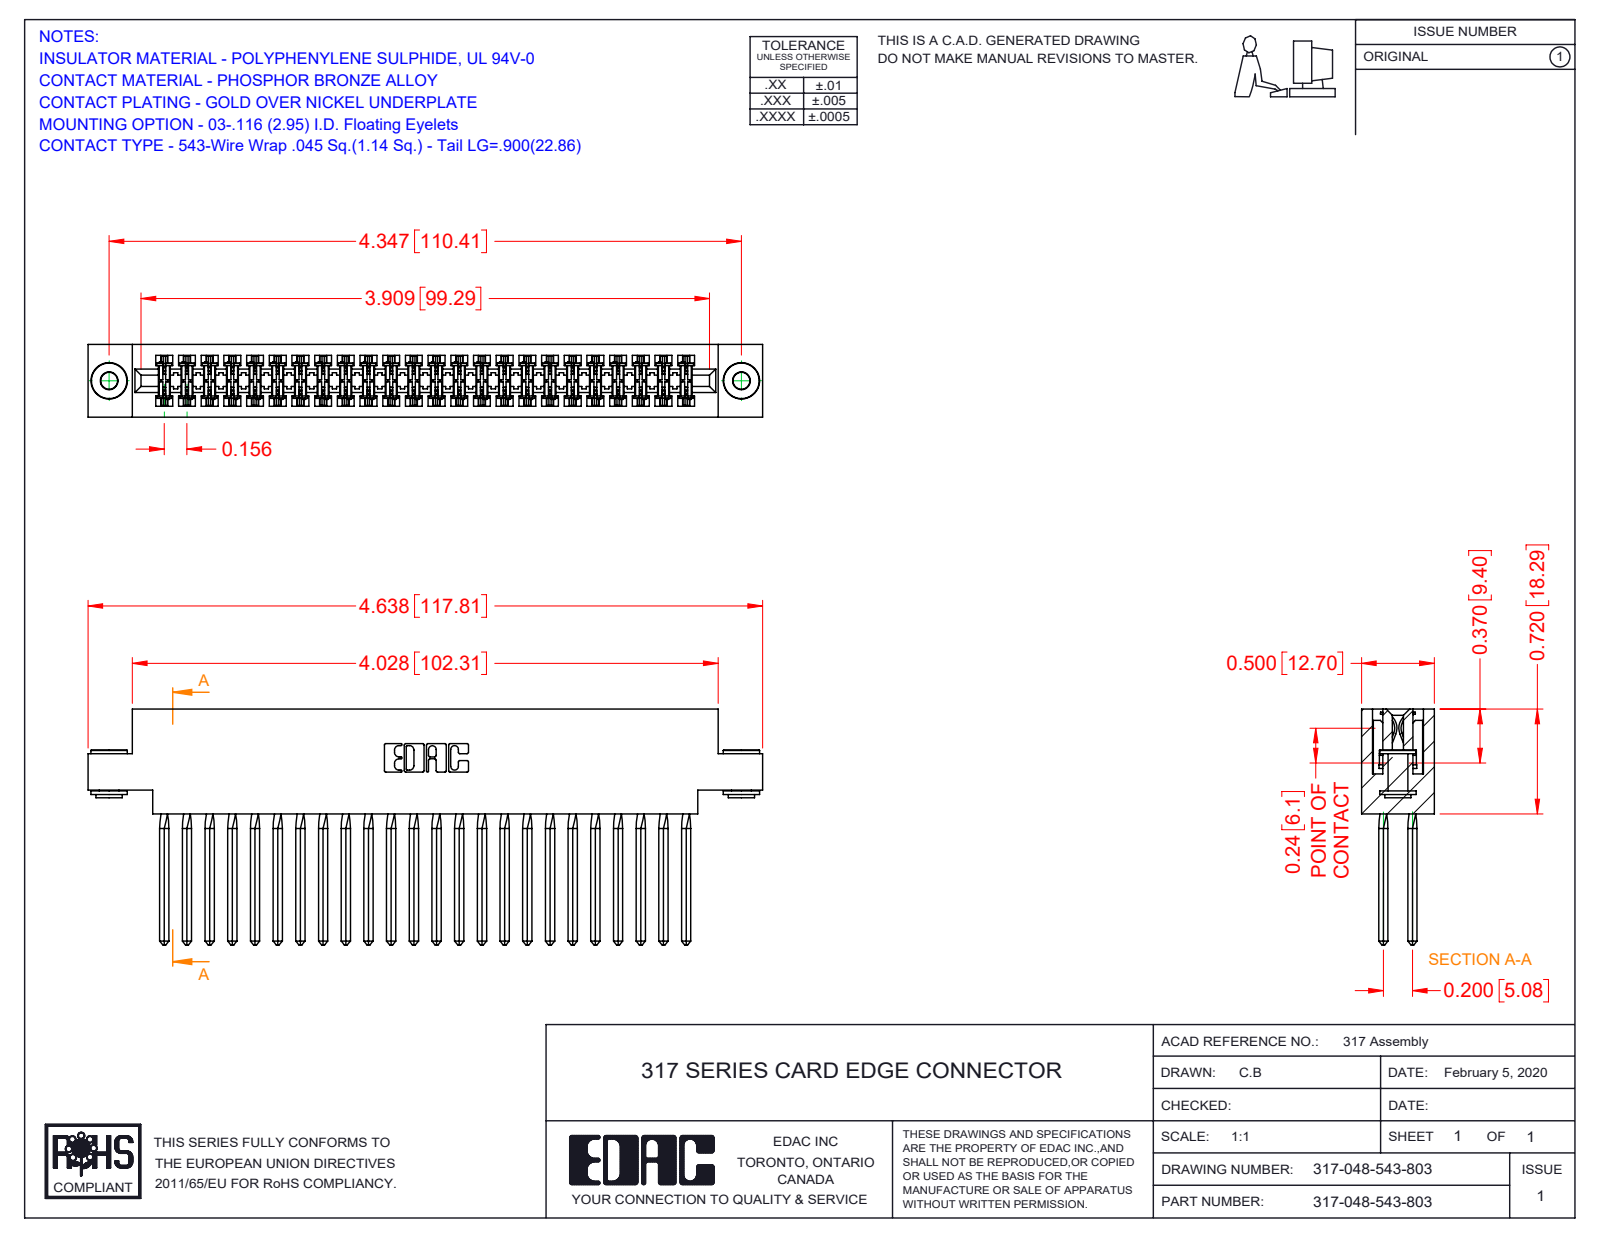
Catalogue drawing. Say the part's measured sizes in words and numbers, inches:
The part is named "317-290-001_543; 345-250-002_345-250-002-102; 317 Part_.156 Dia - TH; 317-048-543-803". Its 3-D file was written by "SolidWorks 2016 (CONFIG_CONTROL_DESIGN)". It is 51 solids with 4412 faces: 3572 planar, 640 cylindrical and 200 other. Overall it measures 4.638 by 1.62 by 0.5 inches. Its volume is 1.185 cubic inches and its surface area 44.9 square inches. Round holes: 2 of diameter 0.116, 2 of diameter 0.156. Round bosses or shafts: 2 of diameter 0.25, 2 of diameter 0.18, 2 of diameter 0.136. Partial cylindrical surfaces (rounded edges, fillets, slot ends): 96 of radius 0.015, 22 of radius 0.01, 6 of radius 0.007, 6 of radius 0.031, 3 of radius 0.026, 2 of radius 0.095, 2 of radius 0.1, 2 of radius 0.11. The main face-to-face distances are 0.5, 0.075, 0.425, 0.11, 0.35, 0.195, 0.22, 0.094, 0.72, 0.2. The hole center spacings are 4.347.
